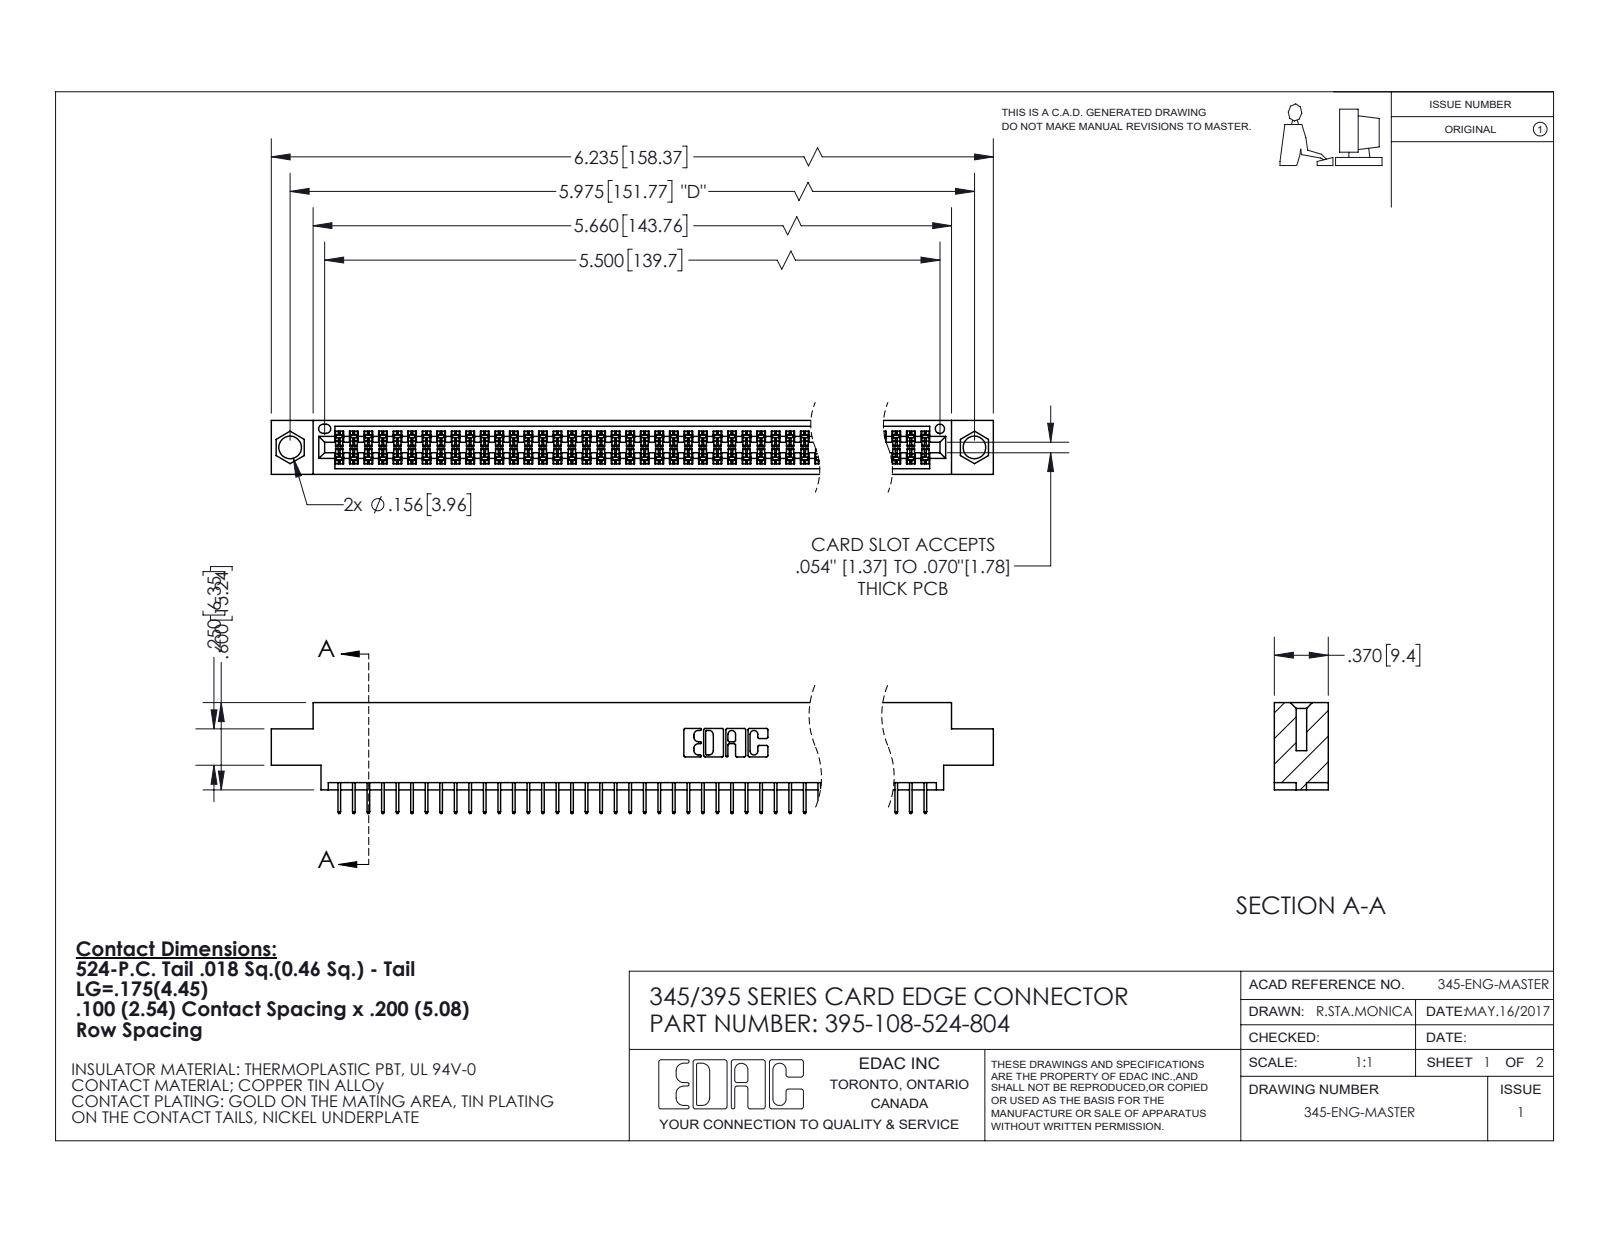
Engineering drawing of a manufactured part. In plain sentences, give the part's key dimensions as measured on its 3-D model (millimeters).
The part is named "395-108-524-804; 345 Part_0.170 Offset - 0.156 Dia-TI; 345-292-001_345-293-124". Its 3-D file was written by "SolidWorks 2020 (CONFIG_CONTROL_DESIGN)". It is 109 solids with 5976 faces: 4310 planar, 1666 cylindrical and 0 other. Overall it measures 158.4 by 19.4 by 9.4 millimeters. Its volume is 15 100 cubic millimeters and its surface area 22 140 square millimeters. Round holes: 2 of diameter 4, 1 of diameter 1.6. Partial cylindrical surfaces (rounded edges, fillets, slot ends): 216 of radius 0.2, 22 of radius 0.3, 6 of radius 0.2, 6 of radius 0.8, 3 of radius 0.7, 2 of radius 0.4, 2 of radius 0.5, 2 of radius 0.6. The main face-to-face distances are 1.8, 7.6, 9.4, 5.1, 2.5, 6.9, 0.6, 5.7, 1.8, 4.4. The hole center spacings are 6.9, 145.8, 151.8.
